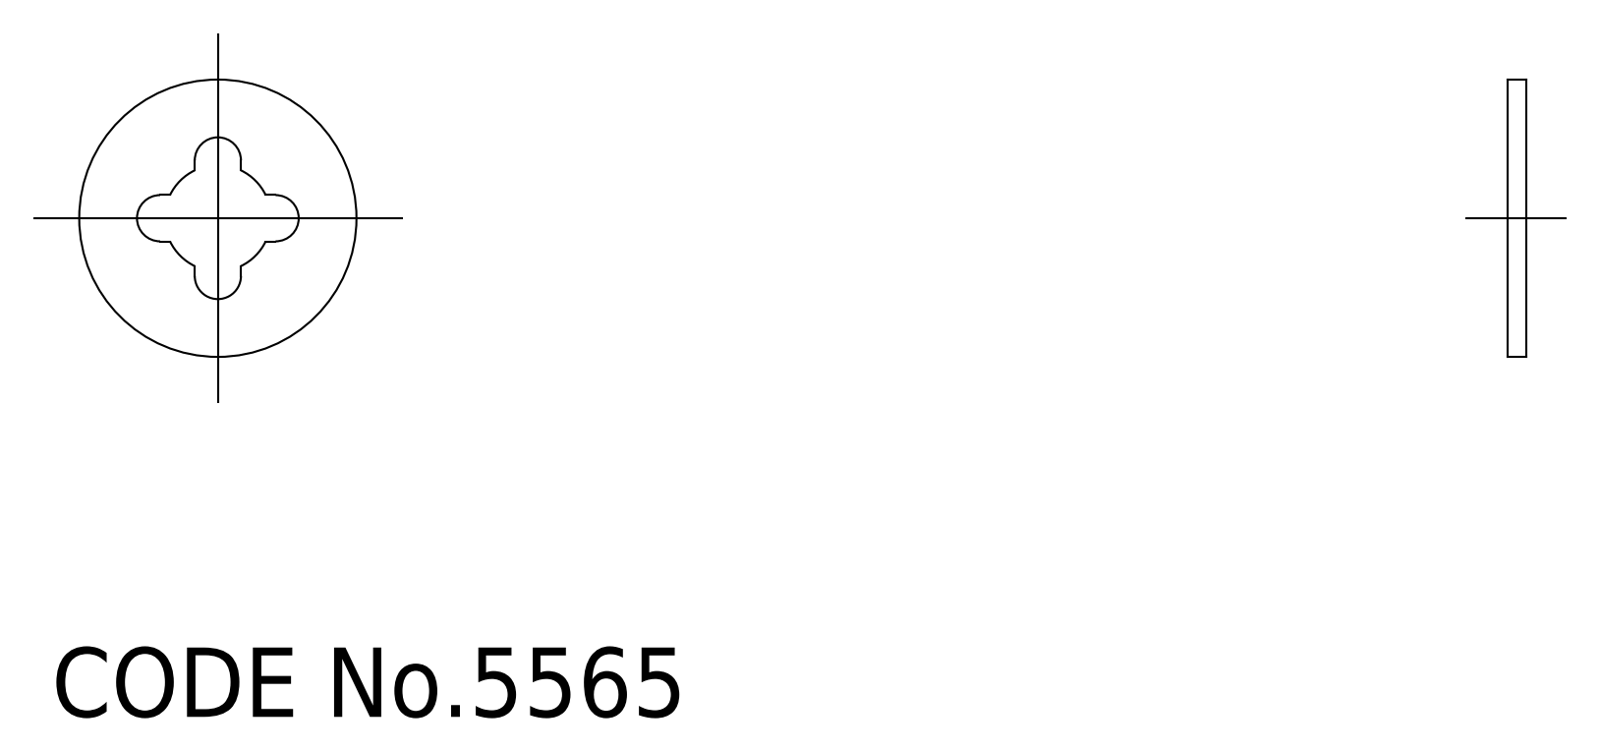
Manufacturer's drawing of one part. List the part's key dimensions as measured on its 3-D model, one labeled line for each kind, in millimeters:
Part name (STEP PRODUCT): washer
STEP written by: CADfix (AUTOMOTIVE_DESIGN)
Units: millimetres
Bodies: 1 solid, 20 faces (0 planar, 0 cylindrical, 20 other)
Overall size (bounding box): 12 × 12 × 0.8
Volume: 71 mm³ · Surface area: 224 mm²
